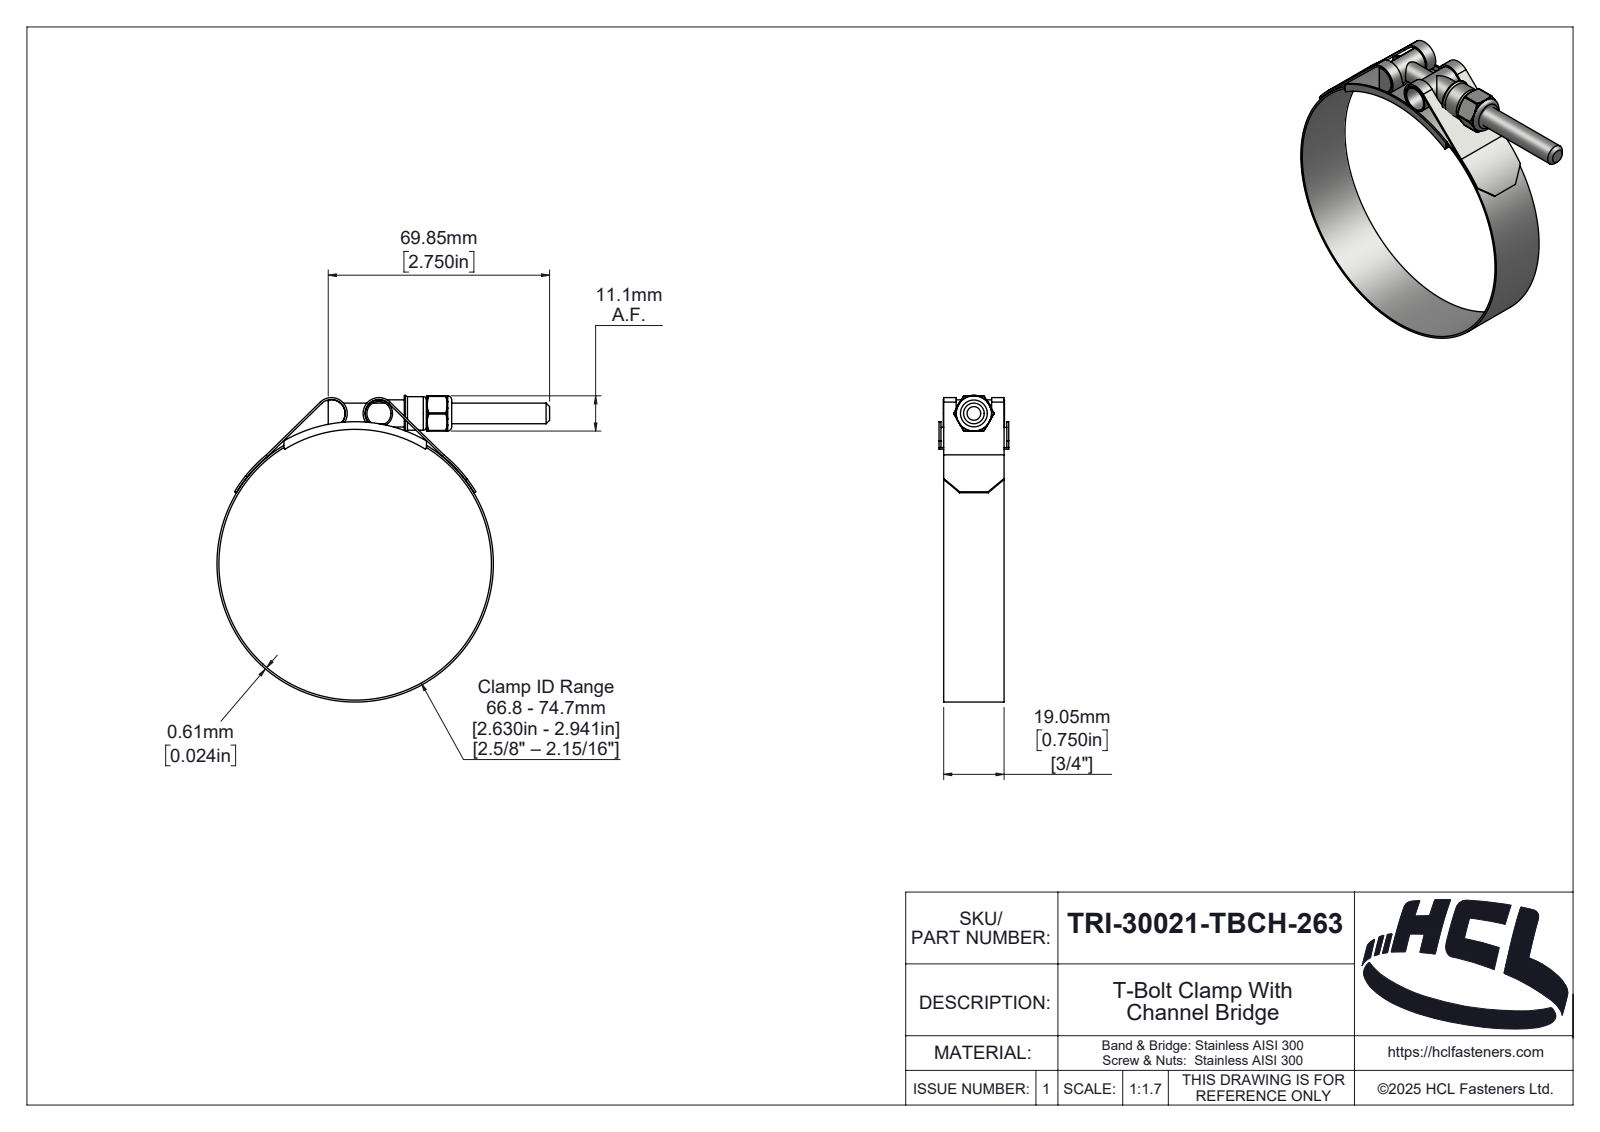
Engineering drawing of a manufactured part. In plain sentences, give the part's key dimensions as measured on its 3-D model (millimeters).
The part is named "TRI-30021-TBCH-263". Its 3-D file was written by "SolidWorks 2025 (AUTOMOTIVE_DESIGN)". It is 6 solids with 330 faces: 46 planar, 122 cylindrical and 162 other. Overall it measures 104.96 by 96.74 by 22 millimeters. Its volume is 8 870 cubic millimeters and its surface area 20 334 square millimeters. Round holes: 1 of diameter 5.4, 1 of diameter 6.35, 1 of diameter 6.5, 1 of diameter 7.58, 1 of diameter 86. Round bosses or shafts: 2 of diameter 8.58, 1 of diameter 87.22, 1 of diameter 10.58. Partial cylindrical surfaces (rounded edges, fillets, slot ends): 6 of radius 0.39, 2 of radius 0.5, 2 of radius 4.39, 2 of radius 5, 1 of radius 0.59, 1 of radius 2.42, 1 of radius 3.03, 1 of radius 3.19. The main face-to-face distances are 0.61, 1.47, 20.53, 19.06, 21.39, 0.86, 19.92, 0.74, 22, 1.35. The hole center spacings are 48.
